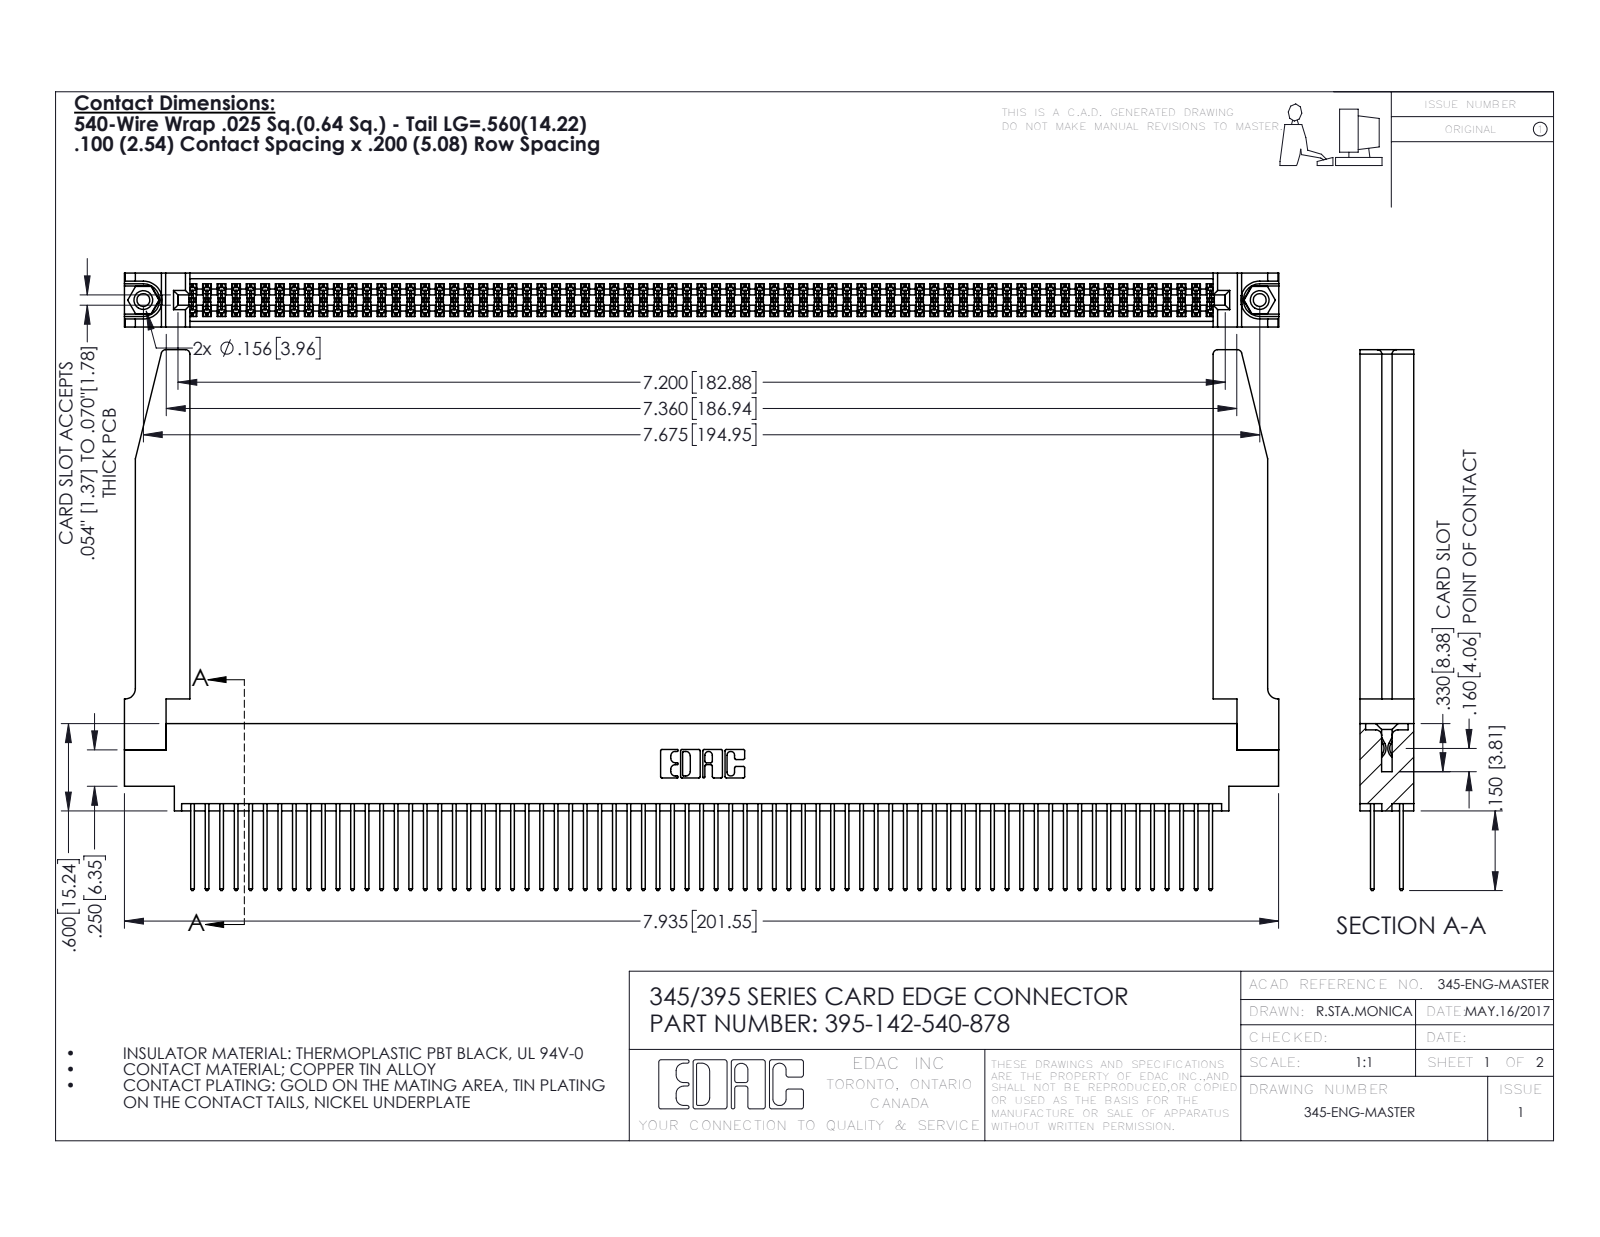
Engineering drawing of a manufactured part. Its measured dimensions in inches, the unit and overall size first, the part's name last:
Units: inches
Overall size (bounding box): 7.936 × 3.717 × 0.37
Round holes (diameter × count): ⌀0.089 ×2, ⌀0.125 ×2, ⌀0.156 ×2, ⌀0.064 ×1
Round bosses / shafts (diameter × count): ⌀0.155 ×2
Partial cylindrical surfaces — rounded edges, fillets, slot ends (radius × count): R0.006 ×213, R0.01 ×142, R0.01 ×22, R0.03 ×8, R0.007 ×6, R0.031 ×6, R0.026 ×3, R0.014 ×2
Main face-to-face distances: 0.072, 0.298, 0.37, 0.098, 0.272, 0.025, 0.2, 0.225, 0.175, 0.149
Hole centre spacings: 0.27, 7.439, 7.675
Volume: 1.711 in³ · Surface area: 62.02 in²
Bodies: 147 solids, 7464 faces (4912 planar, 2500 cylindrical, 52 other)
Part name (STEP PRODUCT): 345-250-001_345-250-001-102; 345 Part_0.170 Offset - 0.156 Dia-TH; 345-292-001_345-293-140; 395-142-540-878 (+1 more)
STEP written by: SolidWorks 2016 (CONFIG_CONTROL_DESIGN)
